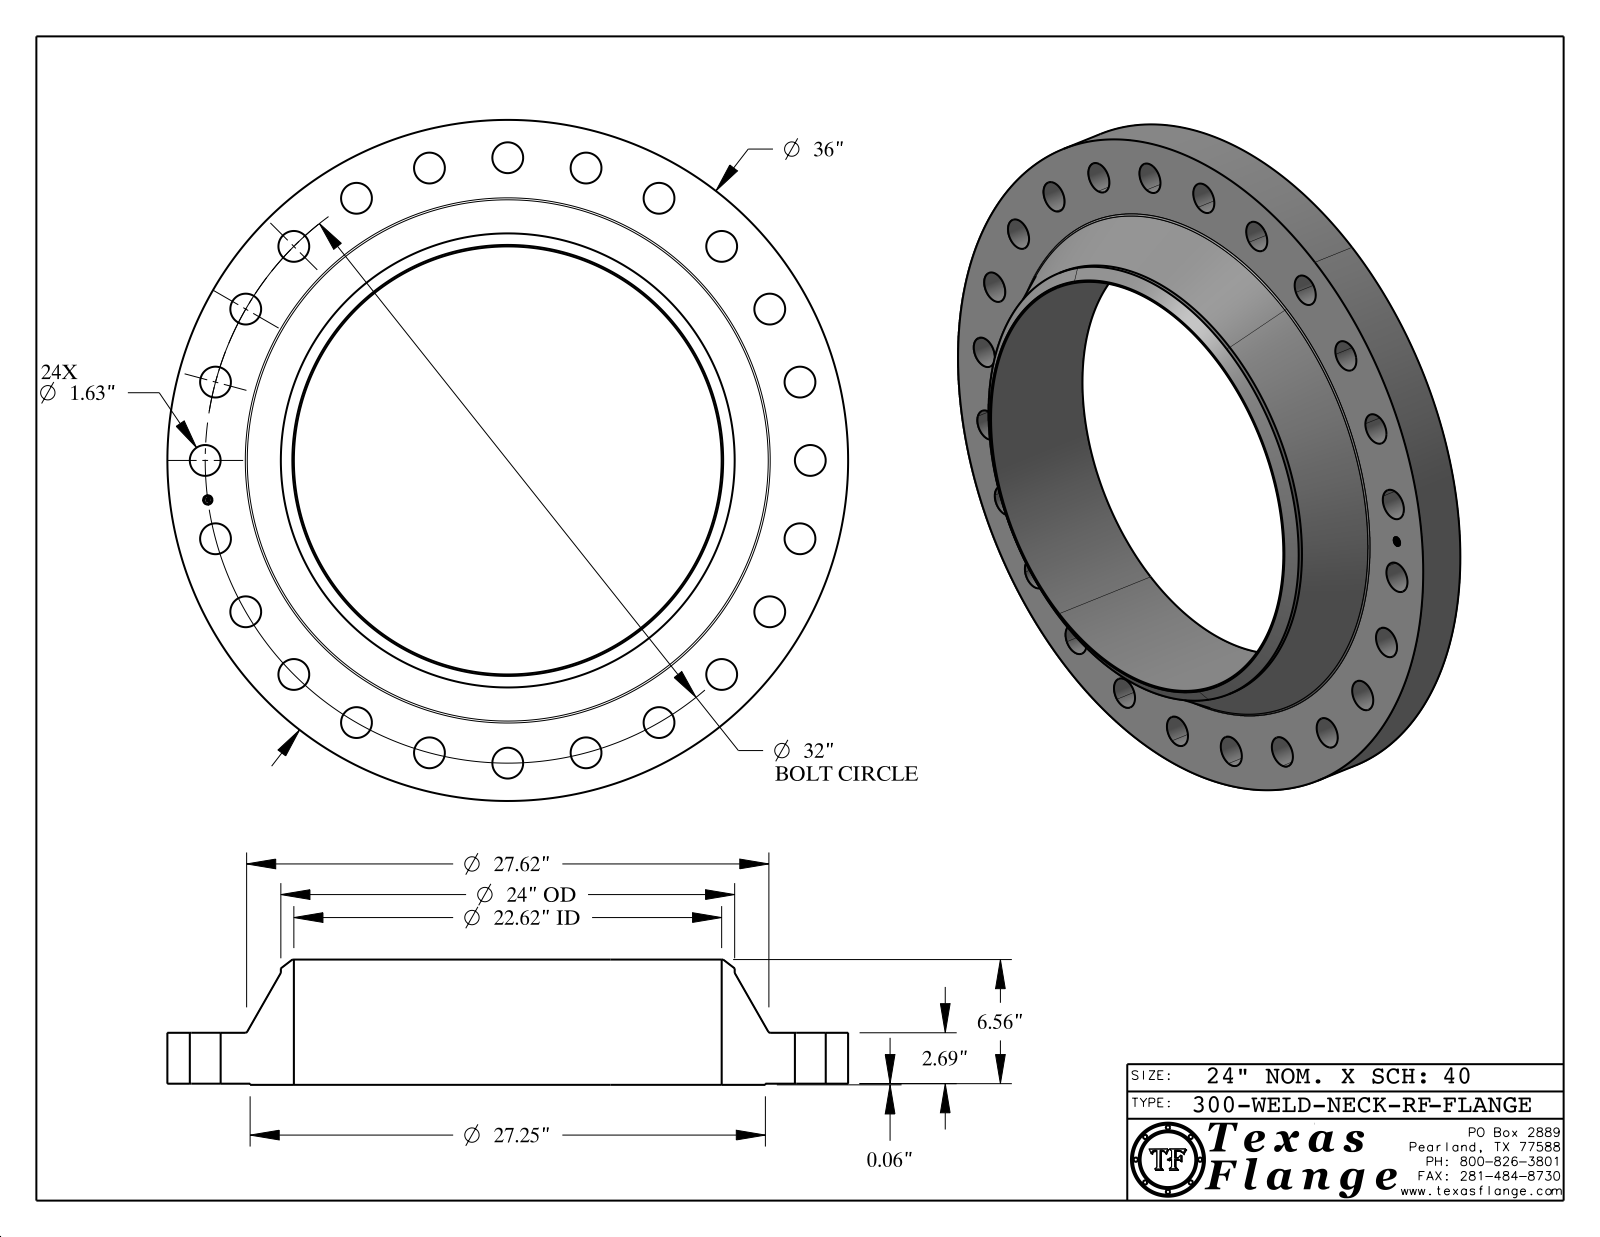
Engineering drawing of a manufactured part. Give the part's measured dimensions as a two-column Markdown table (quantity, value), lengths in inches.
| quantity | value |
| --- | --- |
| part name | 300-WELD-NECK-RF |
| STEP written by | CATIA V5 STEP AP214 (AUTOMOTIVE_DESIGN) |
| units | inches |
| bodies | 1 solid, 451 faces (369 planar, 76 cylindrical, 6 other) |
| overall size | 36 × 36 × 6.623 |
| volume | 1 945 in³ |
| surface area | 2 420 in² |
| round holes (diameter × count) | 1.63 × 24, 0.495 × 1, 22.624 × 1 |
| round bosses / shafts (diameter × count) | 0.03 × 8, 36 × 1, 27.25 × 1, 24 × 1, 0.39 × 1 |
| main face-to-face distances | 2.69, 0.063, 2.753, 6.622, 6.56, 3.87, 2.738, 2.675, 0.015, 3.885 |
| hole center spacings | 16, 30.909, 4.177, 8.282, 12.246, 19.48, 22.627, 25.387 |
